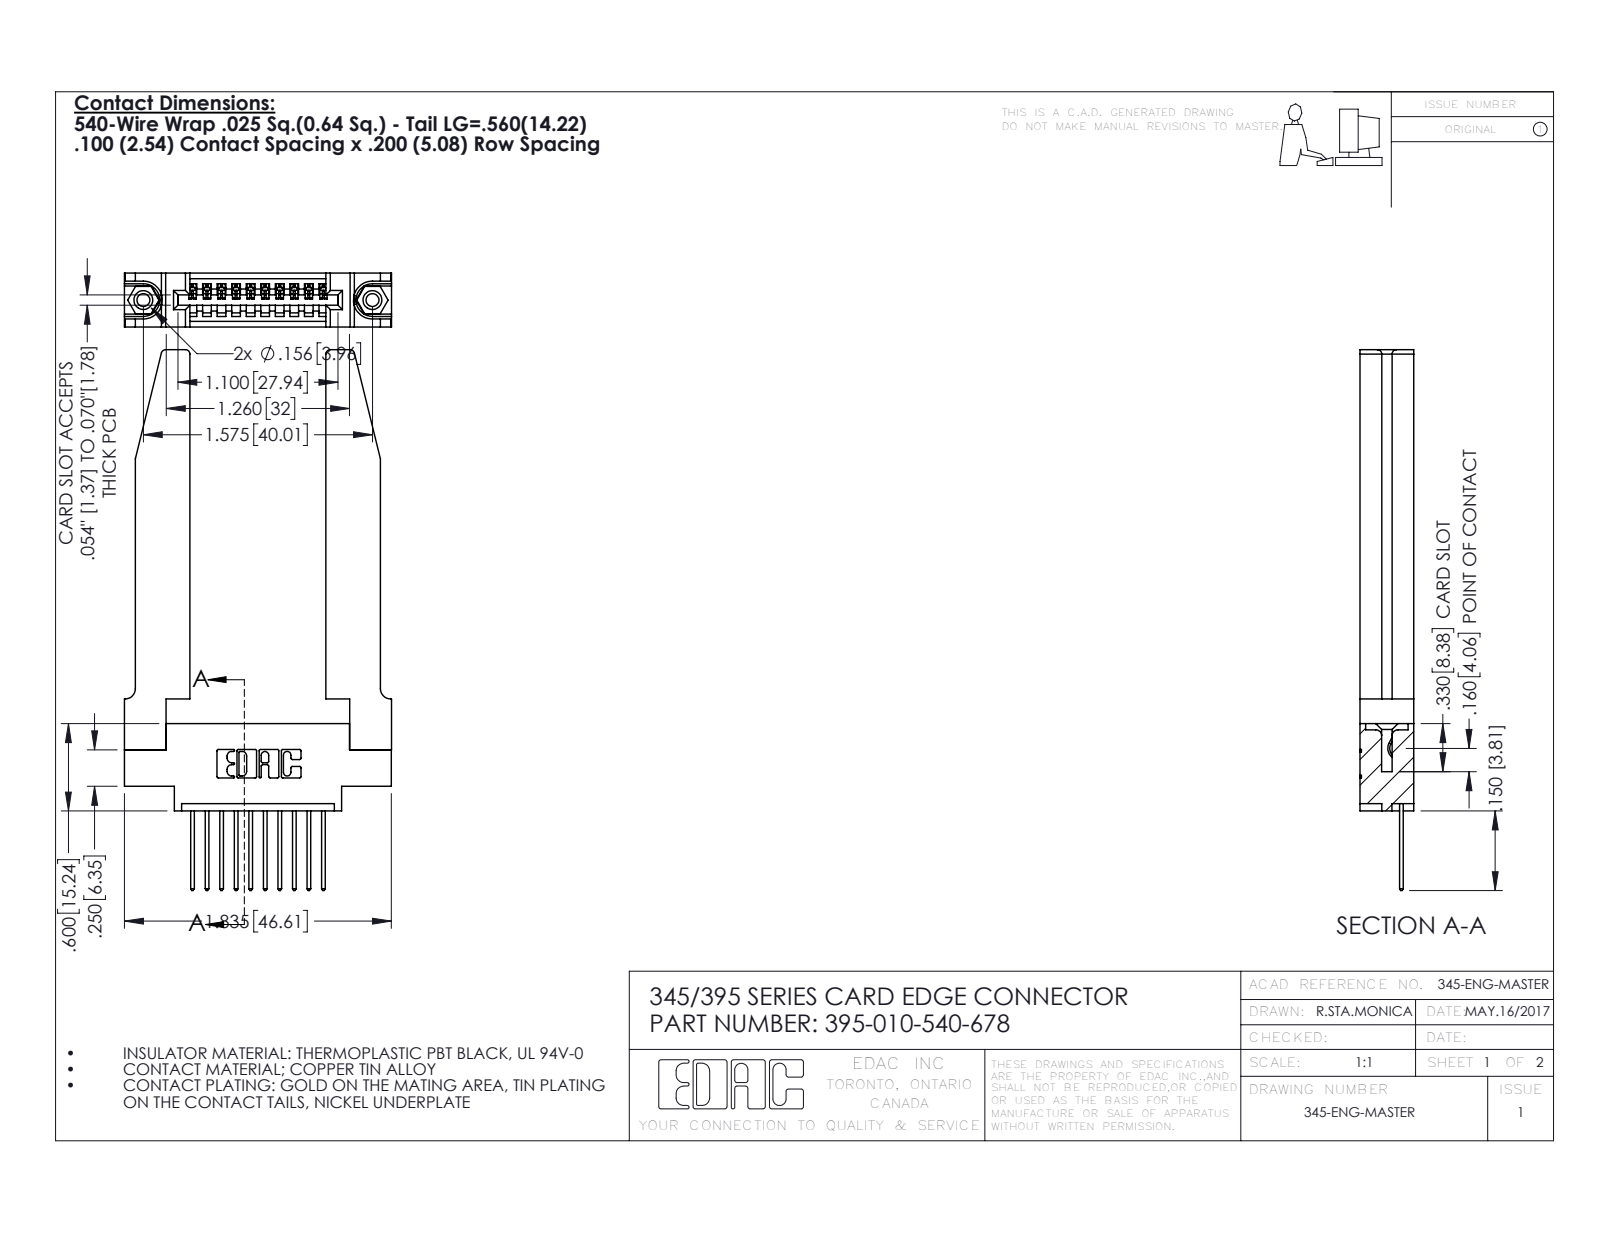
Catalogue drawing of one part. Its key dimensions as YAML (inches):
part_name: "345-292-001_345-293-140; 345-220-078_345-220-078; 345 Part_0.170 Offset - 0.156 Dia-TH; 395-010-540-678 (+1 more)"
step_written_by: "SolidWorks 2016 (CONFIG_CONTROL_DESIGN)"
units: inches
bodies: {solids: 15, faces: 944, planar: 626, cylindrical: 266, other: 52}
overall_size: [3.717, 1.836, 0.37]
volume: 0.722
surface_area: 18.66
round_holes:
  - {diameter: 0.089, count: 2}
  - {diameter: 0.125, count: 2}
  - {diameter: 0.156, count: 2}
  - {diameter: 0.064, count: 1}
round_bosses_or_shafts:
  - {diameter: 0.155, count: 2}
partial_cylinders:
  - {radius: 0.01, count: 22}
  - {radius: 0.006, count: 20}
  - {radius: 0.01, count: 20}
  - {radius: 0.03, count: 8}
  - {radius: 0.007, count: 6}
  - {radius: 0.031, count: 6}
  - {radius: 0.026, count: 3}
  - {radius: 0.031, count: 2}
face_to_face_distances: [0.37, 0.072, 0.298, 0.15, 0.148, 0.22, 0.077, 0.935, 0.2, 0.098]
hole_center_spacings: [0.27, 1.344, 1.575]
